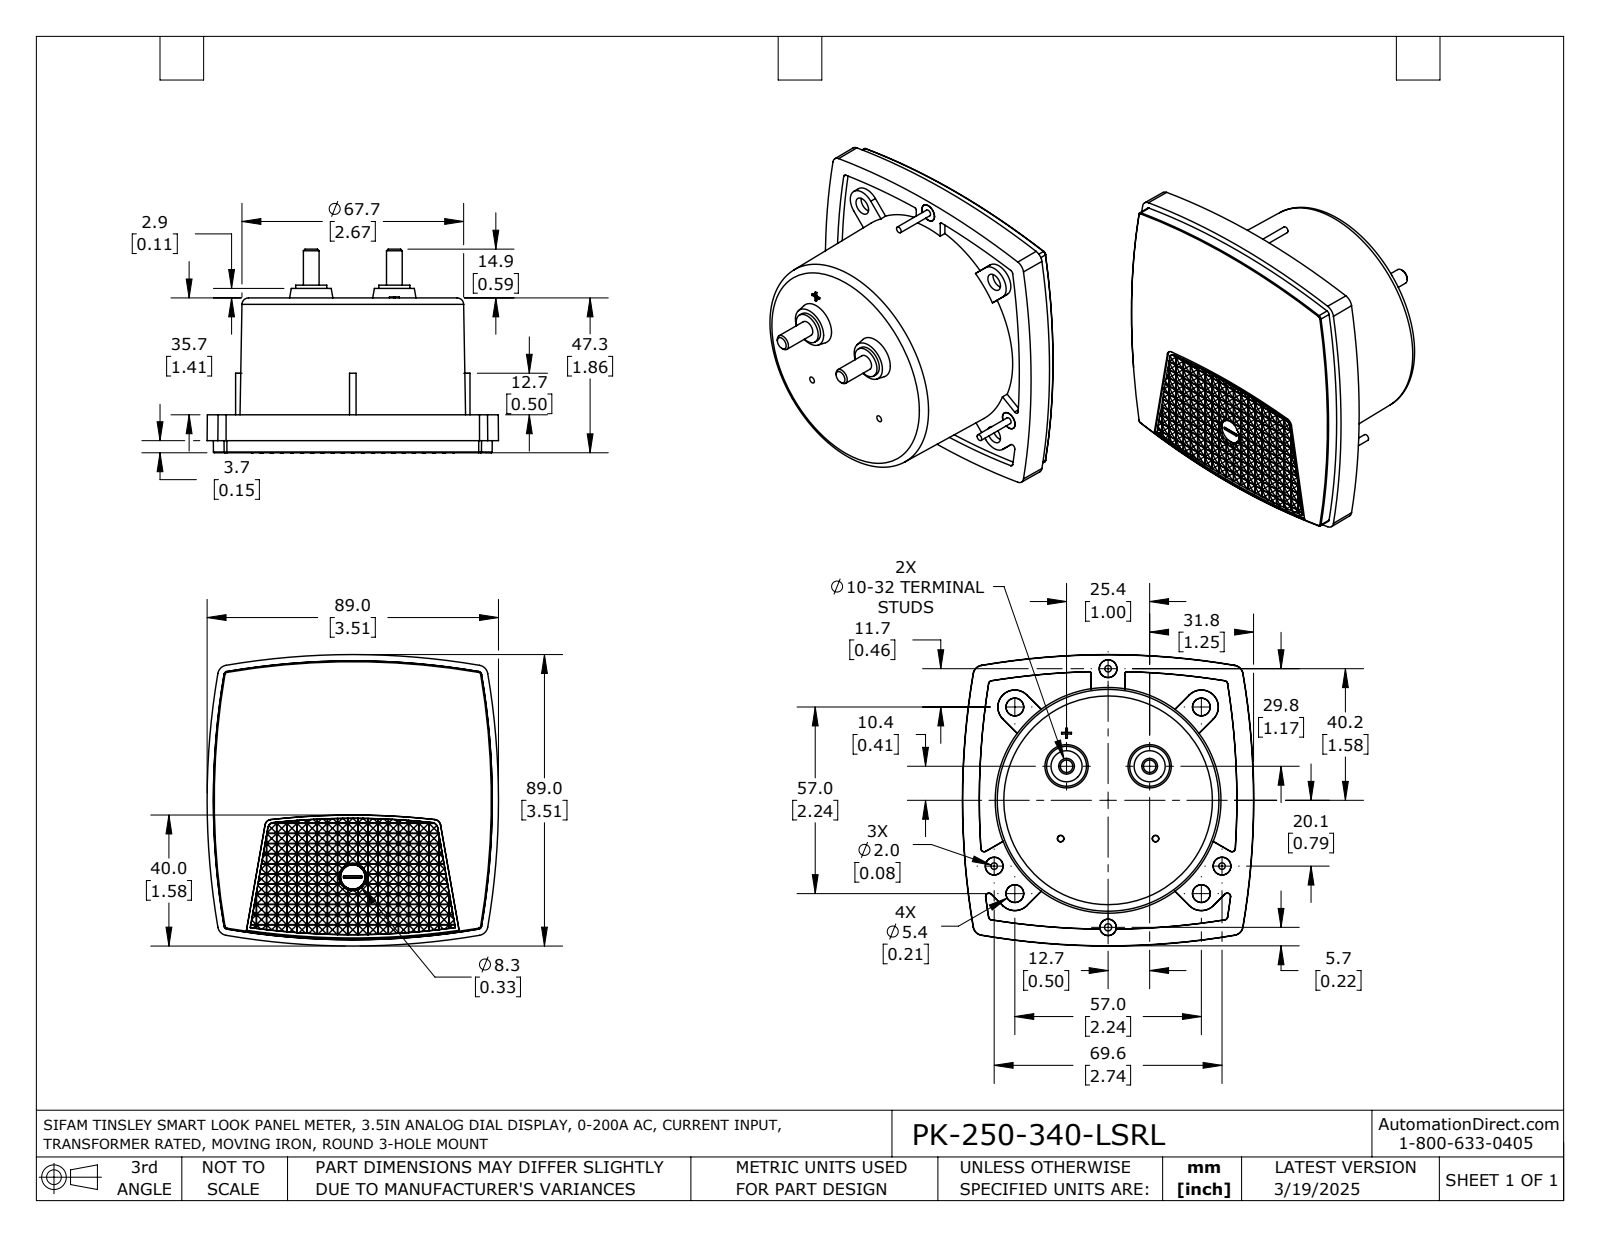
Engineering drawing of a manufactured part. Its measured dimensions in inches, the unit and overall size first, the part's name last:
Units: inches
Overall size (bounding box): 3.505 × 3.505 × 2.453
Round holes (diameter × count): ⌀0.087 ×1
Round bosses / shafts (diameter × count): ⌀0.213 ×3, ⌀0.079 ×3, ⌀0.374 ×2, ⌀0.189 ×2
Partial cylindrical surfaces — rounded edges, fillets, slot ends (radius × count): R8.961 ×1
Main face-to-face distances: 1.862, 1.406, 0.457, 0.079, 1.484, 0.378, 0.024, 0.096, 0.072, 0.12
Volume: 12.99 in³ · Surface area: 44.29 in²
Bodies: 1 solid, 1078 faces (950 planar, 23 cylindrical, 105 other)
Part name (STEP PRODUCT): PK-250-340-LSRL
STEP written by: SolidWorks 2021 (AUTOMOTIVE_DESIGN)
